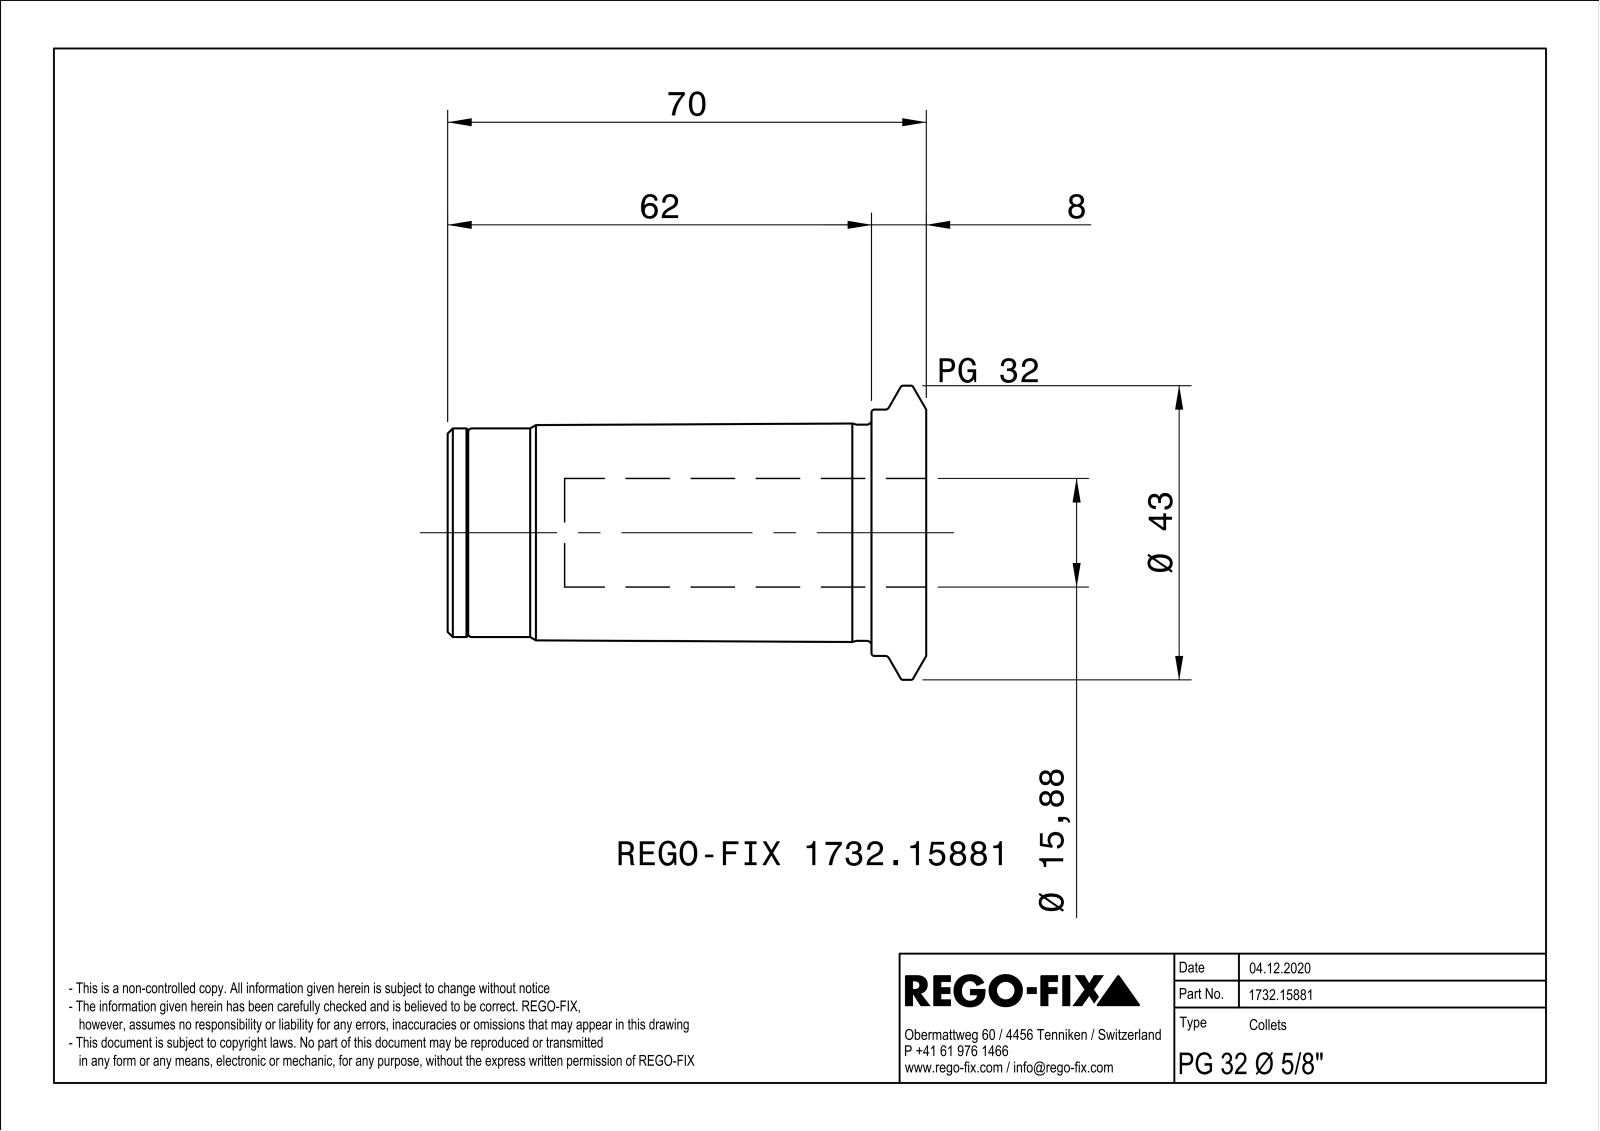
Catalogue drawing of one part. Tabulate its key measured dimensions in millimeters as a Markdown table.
| quantity | value |
| --- | --- |
| part name | NOCUT |
| STEP written by | SIEMENS PLM Software Solid Edge ST10 (AUTOMOTIVE_DESIGN) |
| units | millimeters |
| bodies | 1 solid, 125 faces (31 planar, 40 cylindrical, 54 other) |
| overall size | 70 × 43 × 42.99 |
| volume | 41 958 mm³ |
| surface area | 16 546 mm² |
| round holes (diameter × count) | 4 × 3, 8.92 × 1, 10.5 × 1, 15.88 × 1, 26.92 × 1, 28.5 × 1 |
| round bosses / shafts (diameter × count) | 43 × 1, 36 × 1, 31.6 × 1, 30.5 × 1, 26.5 × 1, 21 × 1 |
| partial cylindrical surfaces (radius × count) | 2 × 6, 3.5 × 3, 3.98 × 1, 4.75 × 1, 8.75 × 1 |
| main face-to-face distances | 1, 70, 58, 12, 59, 11, 8, 60, 2, 10 |
| hole center spacings | 7.75, 13.42, 13.43 |
